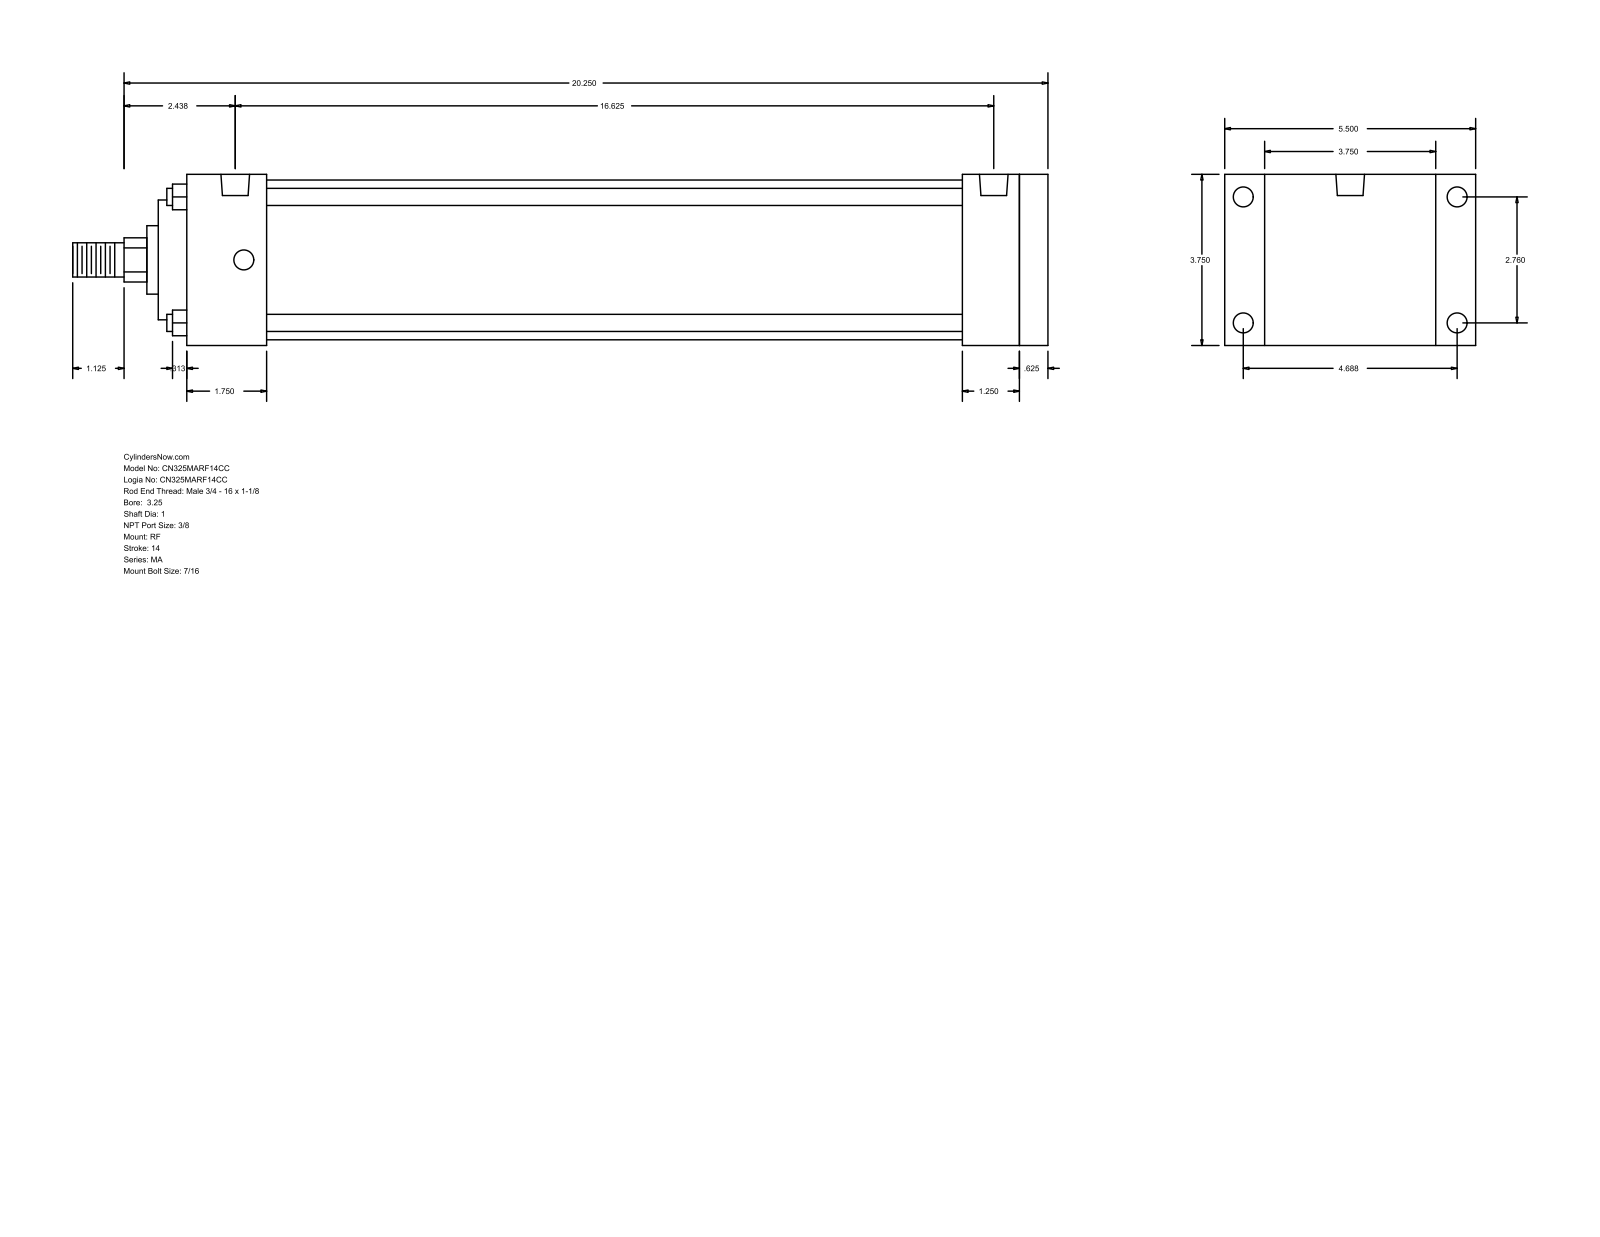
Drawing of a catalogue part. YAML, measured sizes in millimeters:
part_name: "MA_RF__0325_1"
step_written_by: "GSSL Pune (CONFIG_CONTROL_DESIGN)"
units: millimeters
bodies: {solids: 0, faces: 94, planar: 65, cylindrical: 29, other: 0}
overall_size: [542.92, 139.7, 95.25]
round_holes:
  - {diameter: 11.11, count: 8}
  - {diameter: 15.93, count: 2}
round_bosses_or_shafts:
  - {diameter: 9.53, count: 4}
  - {diameter: 88.9, count: 1}
  - {diameter: 66.67, count: 1}
  - {diameter: 38.1, count: 1}
  - {diameter: 25.4, count: 1}
  - {diameter: 19.05, count: 1}
partial_cylinders:
  - {radius: 12.29, count: 1}
face_to_face_distances: [95.24, 479.43, 15.87, 463.56, 22.23, 117.47, 47.62, 495.3, 431.81, 31.75]
hole_center_spacings: [4.76, 70.1, 119.06, 138.16, 412.76, 417.52, 422.28]
